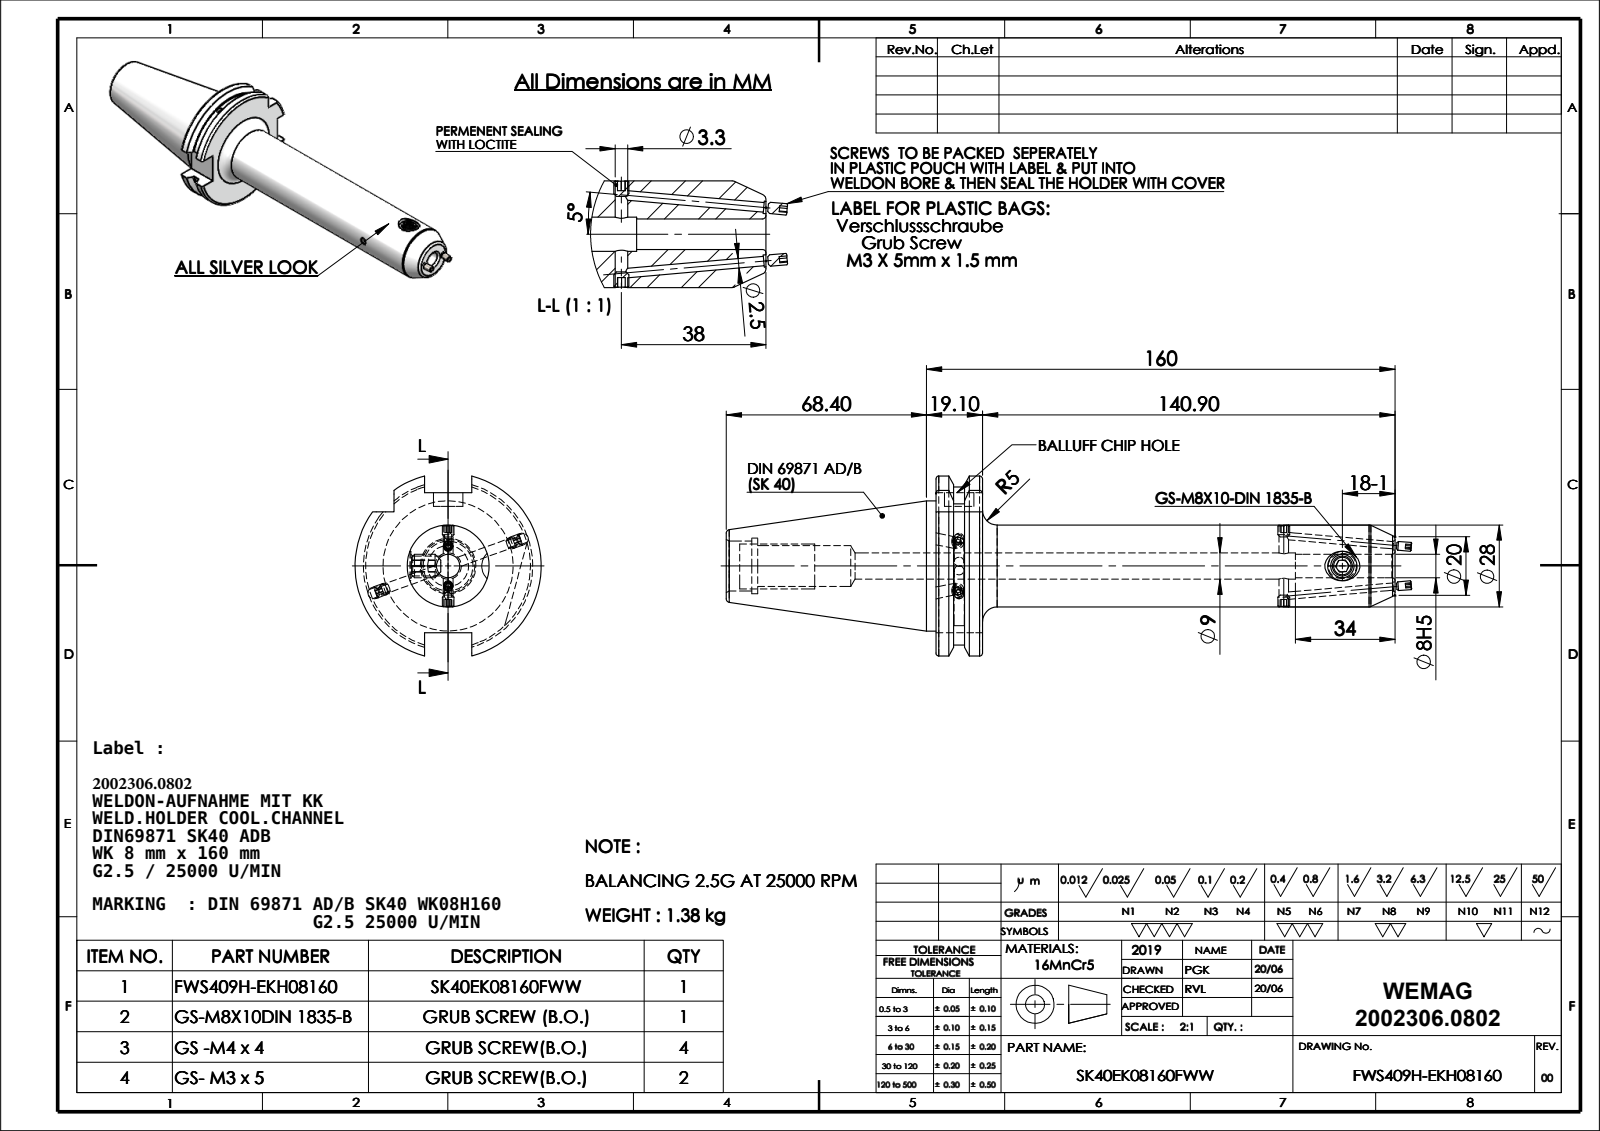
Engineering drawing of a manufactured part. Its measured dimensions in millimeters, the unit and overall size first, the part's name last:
Units: millimetres
Overall size (bounding box): 228.4 × 63.55 × 61.48
Round holes (diameter × count): ⌀2.5 ×2, ⌀3.2 ×2, ⌀3.3 ×2, ⌀10 ×2, ⌀6.8 ×1, ⌀8 ×1, ⌀9 ×1, ⌀14 ×1, ⌀17 ×1, ⌀19 ×1
Round bosses / shafts (diameter × count): ⌀44.45 ×1, ⌀28 ×1
Partial cylindrical surfaces — rounded edges, fillets, slot ends (radius × count): R28.12 ×1, R31.77 ×1
Main face-to-face distances: 15.9, 16.1, 47.8, 156.8, 140.9, 71.6, 87.5, 228.4, 10.7, 60.9
Hole centre spacings: 110.85
Volume: 178 598 mm³ · Surface area: 37 387 mm²
Bodies: 1 solid, 124 faces (32 planar, 48 cylindrical, 44 other)
Part name (STEP PRODUCT): 91406-WK208160
STEP written by: SolidWorks 2018 (CONFIG_CONTROL_DESIGN)
